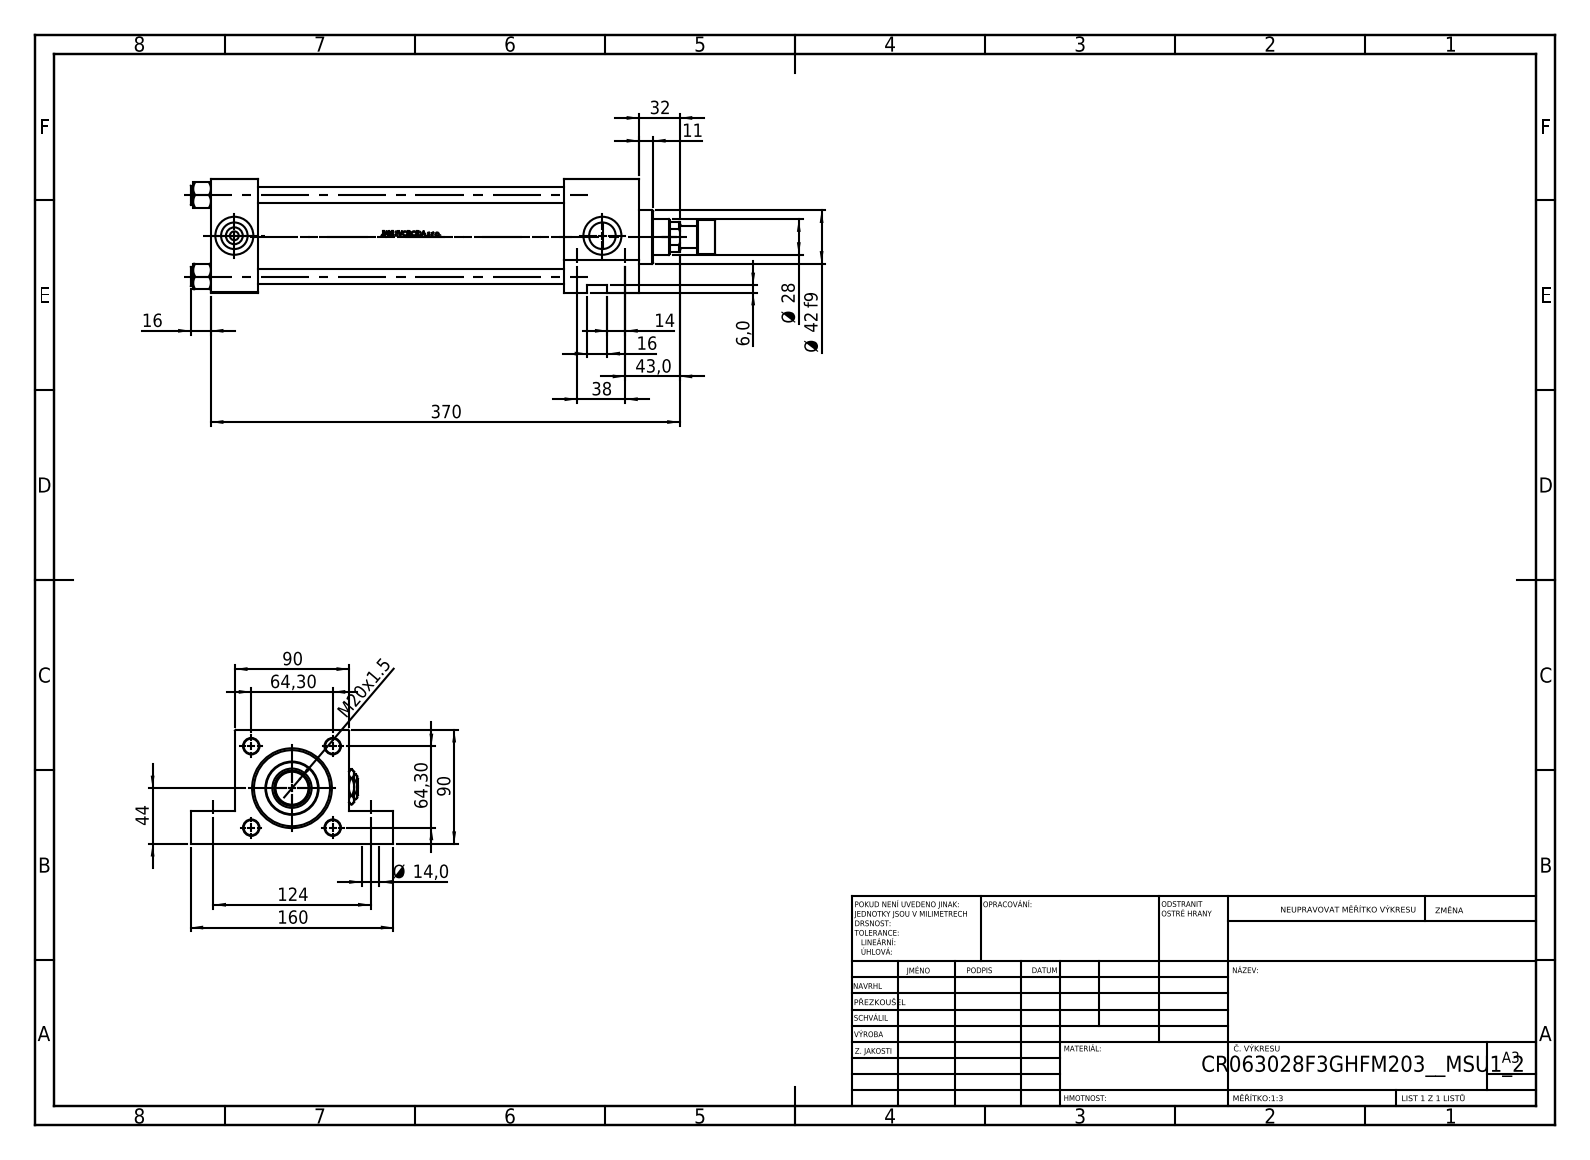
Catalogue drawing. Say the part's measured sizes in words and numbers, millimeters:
The part is named "Zatka_pro_OIL_PORT; V215CR_F_TYCINKA; V215CR_ROD_END_F; V215CR_F_Body (+3 more)". Its 3-D file was written by "SolidWorks 2019 (CONFIG_CONTROL_DESIGN)". It is 14 solids with 1214 faces: 488 planar, 138 cylindrical and 588 other. Overall it measures 414 by 160 by 90 millimeters. Its volume is 1 344 000 cubic millimeters and its surface area 321 496 square millimeters. Round holes: 4 of diameter 12, 4 of diameter 14, 3 of diameter 20.96, 3 of diameter 30, 2 of diameter 7, 1 of diameter 18.5, 1 of diameter 20, 1 of diameter 28, 1 of diameter 31, 1 of diameter 50, 1 of diameter 60, 1 of diameter 63. Round bosses or shafts: 4 of diameter 15, 1 of diameter 69, 1 of diameter 42, 1 of diameter 27, 1 of diameter 18. The main face-to-face distances are 90, 37, 301, 338, 279, 242, 59, 26, 64, 35. The hole center spacings are 64.3, 38, 44.77, 46.18, 90.93, 124, 129.69, 10.
